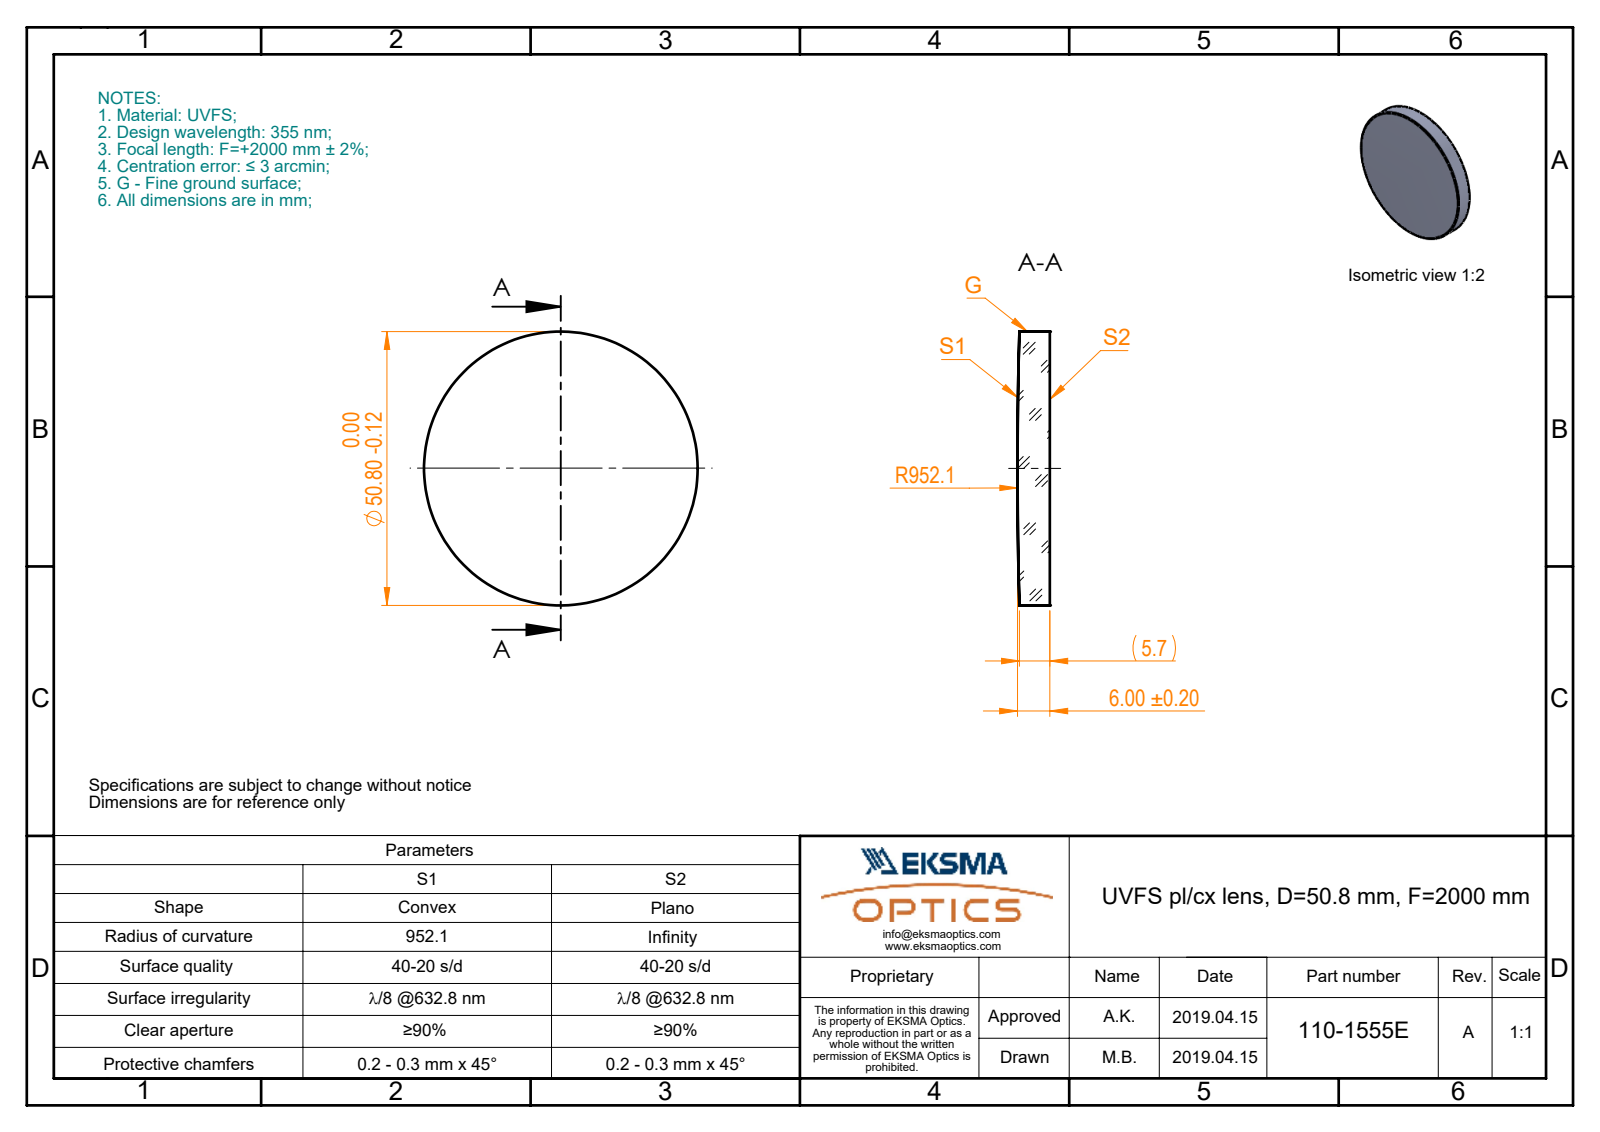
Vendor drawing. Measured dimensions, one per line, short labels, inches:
name: 110-1555E UVFS pl-cx 50.8 F2000
written by: SolidWorks 2017 (CONFIG_CONTROL_DESIGN)
unit: in
bodies: 1 solid, 5 faces (1 planar, 2 cylindrical, 2 other)
size: 2 × 2 × 0.236
volume: 0.721 in³; area: 7.685 in²
bosses: 1× ⌀2
